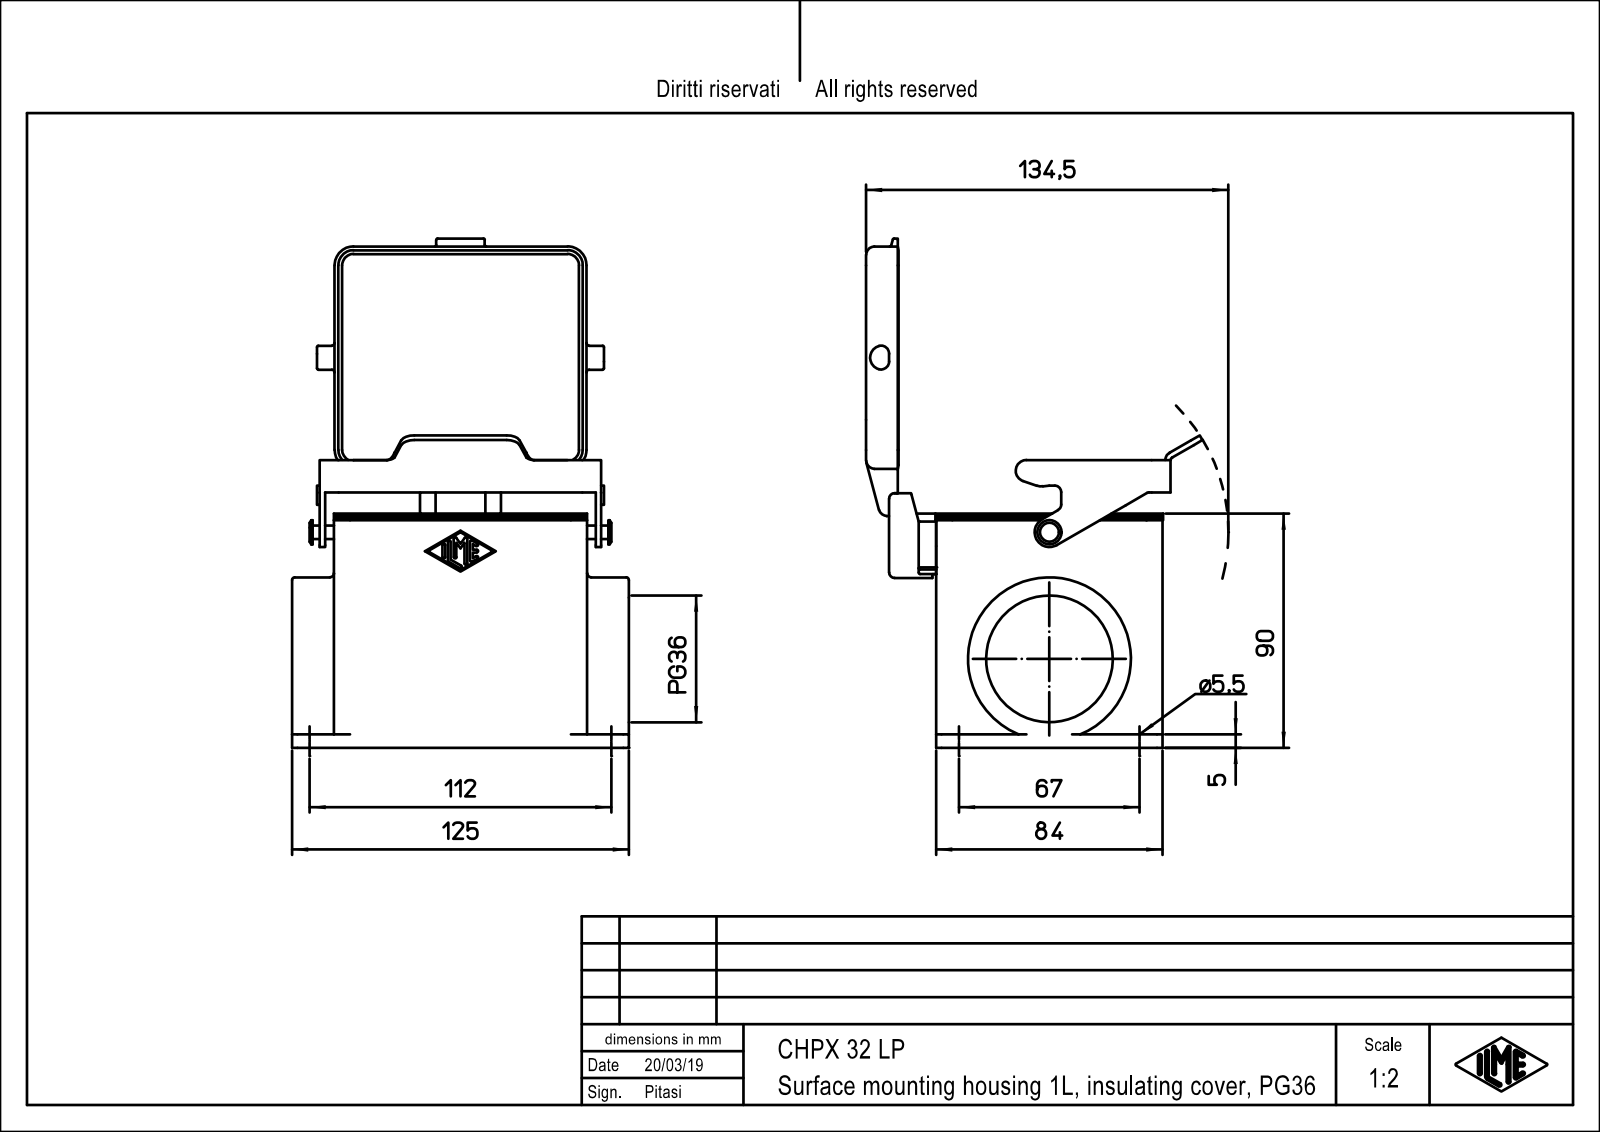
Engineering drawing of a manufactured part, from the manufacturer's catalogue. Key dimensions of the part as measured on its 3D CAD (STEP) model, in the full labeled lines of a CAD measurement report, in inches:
Part name (STEP PRODUCT): CHPX_32_L; CHPX_32_LP; CHPX_32_LP.stp
STEP written by: PTC Creo Elements/Direct Modeling 19.0E 27-Jun-2016 (C) Parametric Technology GmbH (AUTOMOTIVE_DESIGN)
Units: inches
Bodies: 1 solid, 337 faces (178 planar, 139 cylindrical, 20 other)
Overall size (bounding box): 7.441 × 4.921 × 4.916
Volume: 16.13 in³ · Surface area: 199.8 in²
Round holes (diameter × count): ⌀0.118 ×8, ⌀0.217 ×4, ⌀0.165 ×1, ⌀1.181 ×1, ⌀1.85 ×1
Round bosses / shafts (diameter × count): ⌀2.382 ×1, ⌀0.354 ×1, ⌀0.236 ×1, ⌀0.197 ×1
Partial cylindrical surfaces — rounded edges, fillets, slot ends (radius × count): R0.118 ×14, R0.079 ×11, R0.059 ×9, R0.236 ×8, R0.02 ×6, R0.276 ×6, R0.197 ×5, R0.165 ×4
Main face-to-face distances: 0.118, 0.079, 3.189, 0.157, 1.063, 3.307, 4.331, 4.252, 0.945, 1.024
Hole centre spacings: 0.684, 1.063, 1.328, 1.417, 1.643, 2.648, 3.051, 3.231
